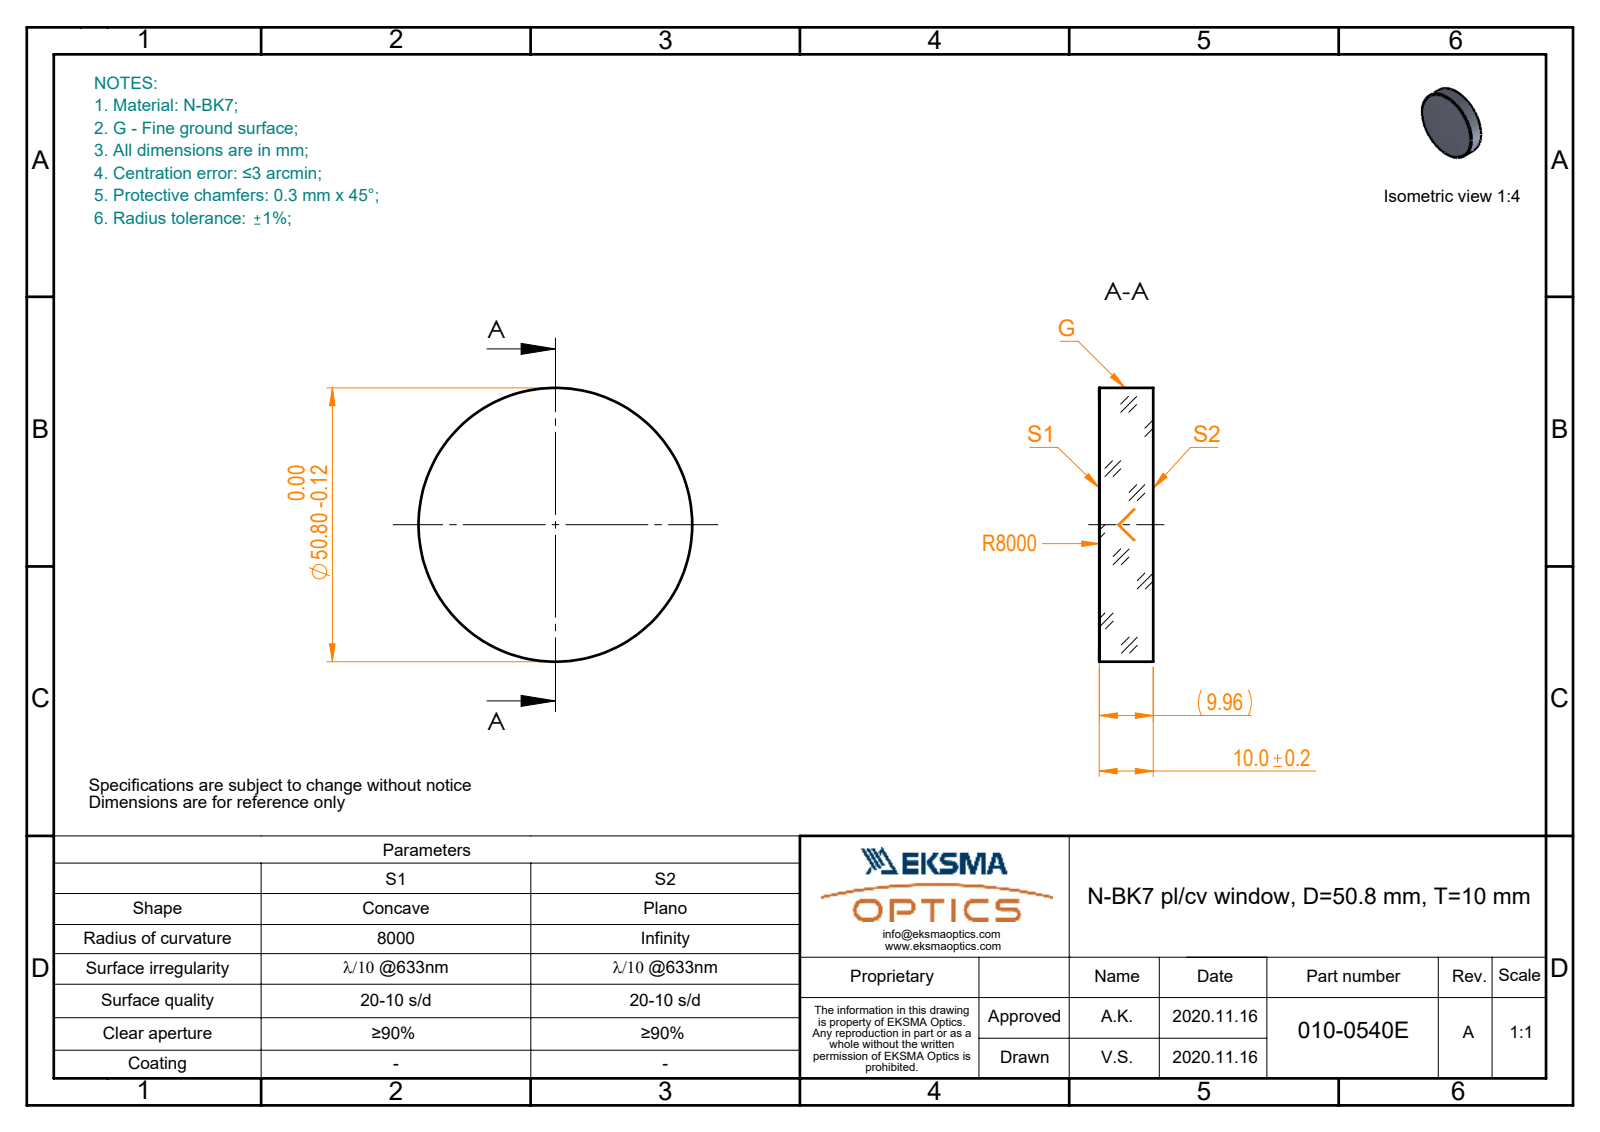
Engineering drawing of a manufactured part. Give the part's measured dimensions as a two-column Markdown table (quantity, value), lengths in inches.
| quantity | value |
| --- | --- |
| part name | 010-0540E_N-BK7_PCV_window |
| STEP written by | SolidWorks 2019 (CONFIG_CONTROL_DESIGN) |
| units | inches |
| bodies | 1 solid, 5 faces (1 planar, 2 cylindrical, 2 other) |
| overall size | 2 × 2 × 0.394 |
| volume | 1.234 in³ |
| surface area | 8.758 in² |
| round bosses / shafts (diameter × count) | 2 × 1 |
